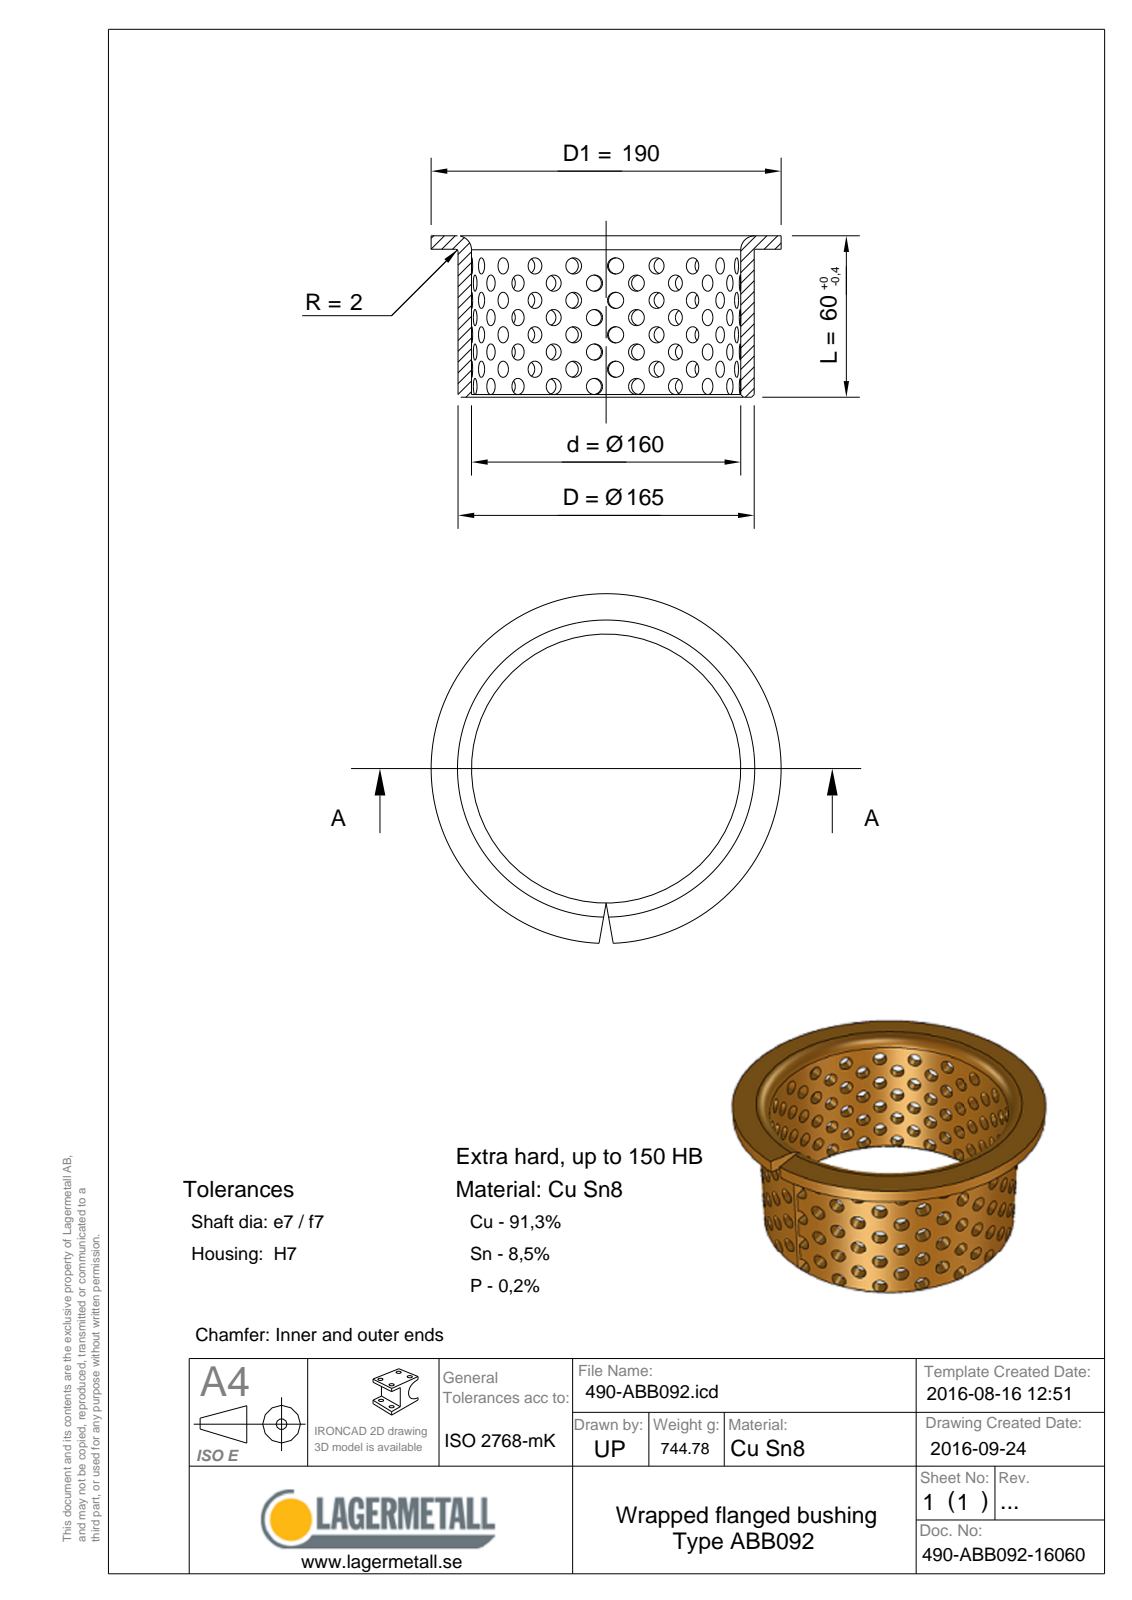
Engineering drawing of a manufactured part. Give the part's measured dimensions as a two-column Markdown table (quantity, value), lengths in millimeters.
| quantity | value |
| --- | --- |
| STEP written by | Spatial InterOp 3D (CONFIG_CONTROL_DESIGN) |
| units | millimeters |
| bodies | 1 solid, 26 faces (5 planar, 9 cylindrical, 12 other) |
| overall size | 190 × 190 × 60 |
| volume | 91 948 mm³ |
| surface area | 76 464 mm² |
| round holes (diameter × count) | 160 × 1 |
| round bosses / shafts (diameter × count) | 190 × 1, 165 × 1 |
| main face-to-face distances | 2.5, 57.5, 60 |
